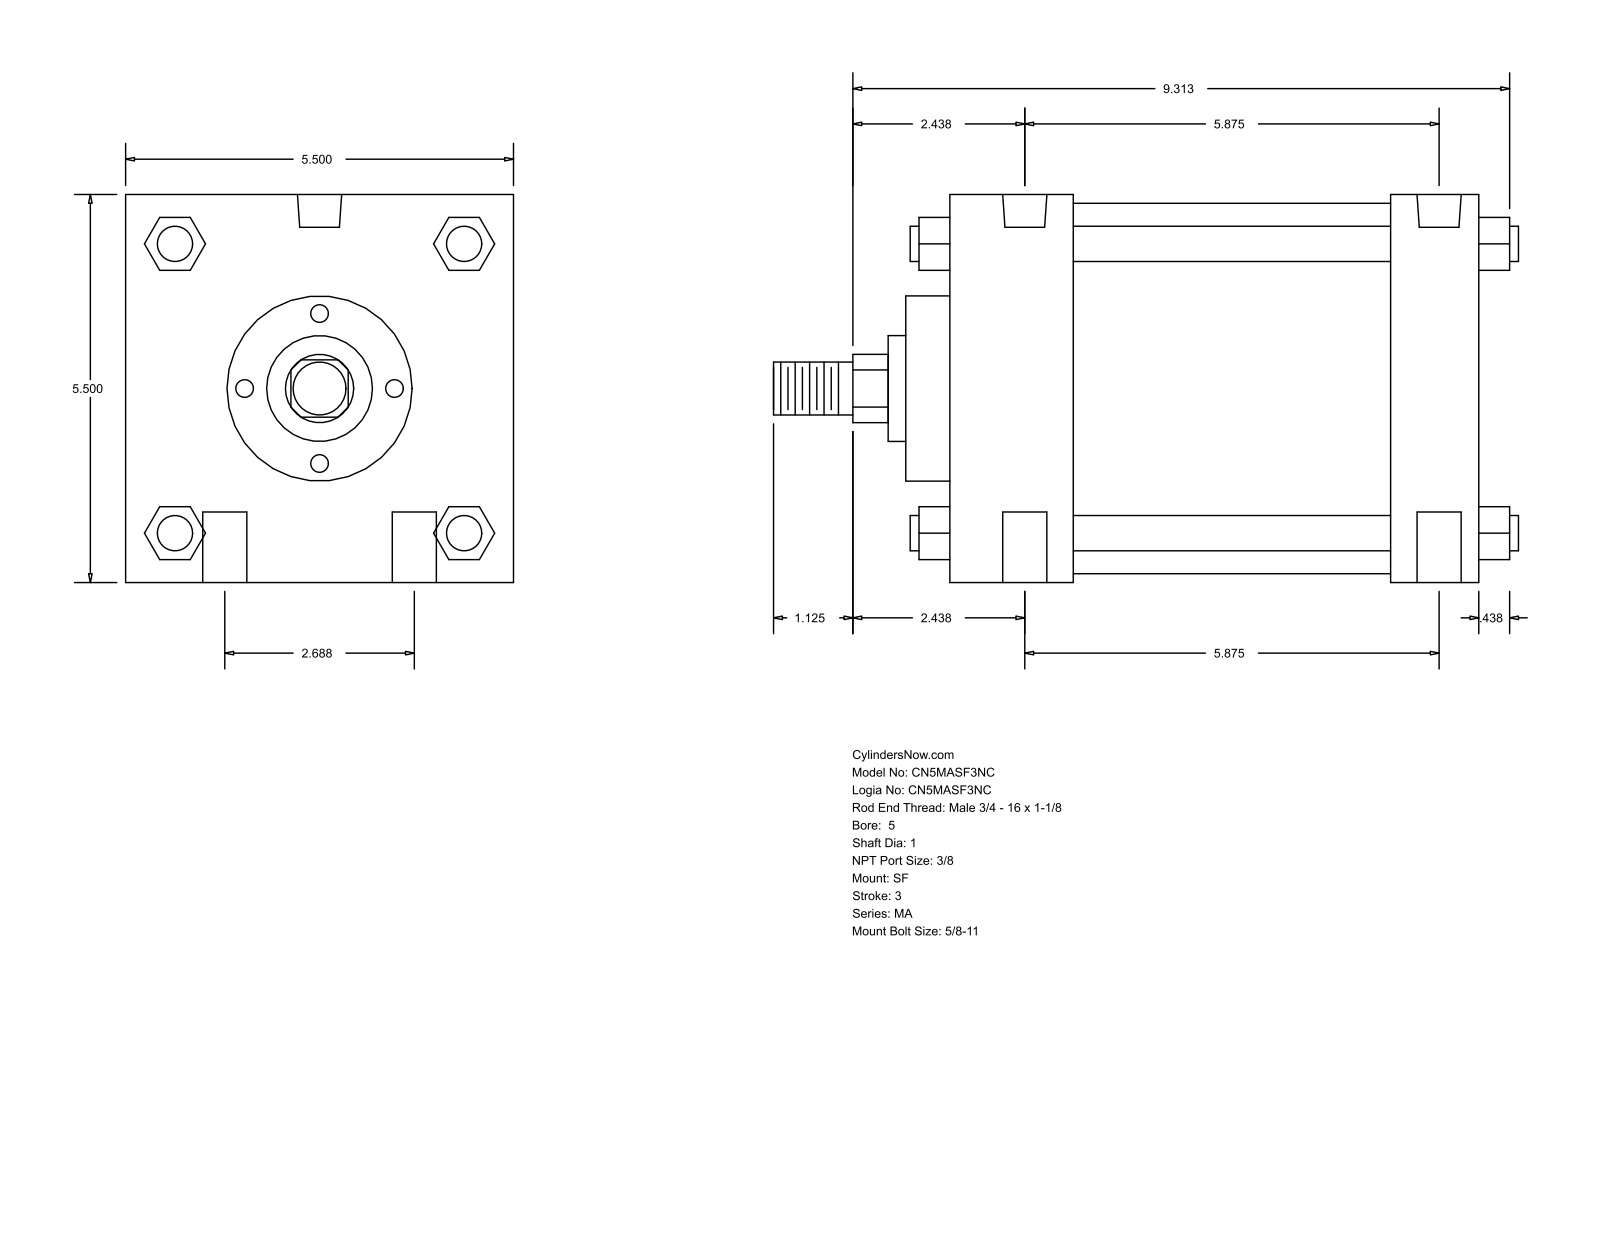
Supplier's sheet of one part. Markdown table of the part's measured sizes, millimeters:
| quantity | value |
| --- | --- |
| part name | MA_SF__0500_1 |
| STEP written by | GSSL Pune (CONFIG_CONTROL_DESIGN) |
| units | millimeters |
| bodies | 0 solids, 126 faces (95 planar, 31 cylindrical, 0 other) |
| overall size | 268.29 × 139.7 × 139.7 |
| round holes (diameter × count) | 15.88 × 4, 11.11 × 2, 15.93 × 2 |
| round bosses / shafts (diameter × count) | 12.7 × 4, 133.35 × 1, 66.67 × 1, 38.1 × 1, 25.4 × 1, 19.05 × 1 |
| partial cylindrical surfaces (radius × count) | 12.29 × 1 |
| main face-to-face distances | 139.7, 190.51, 44.46, 158.76, 114.3, 146.05, 31.75, 15.87, 60.33, 174.63 |
| hole center spacings | 34.13, 153.08, 149.23, 68.26, 164.1, 139.71 |
